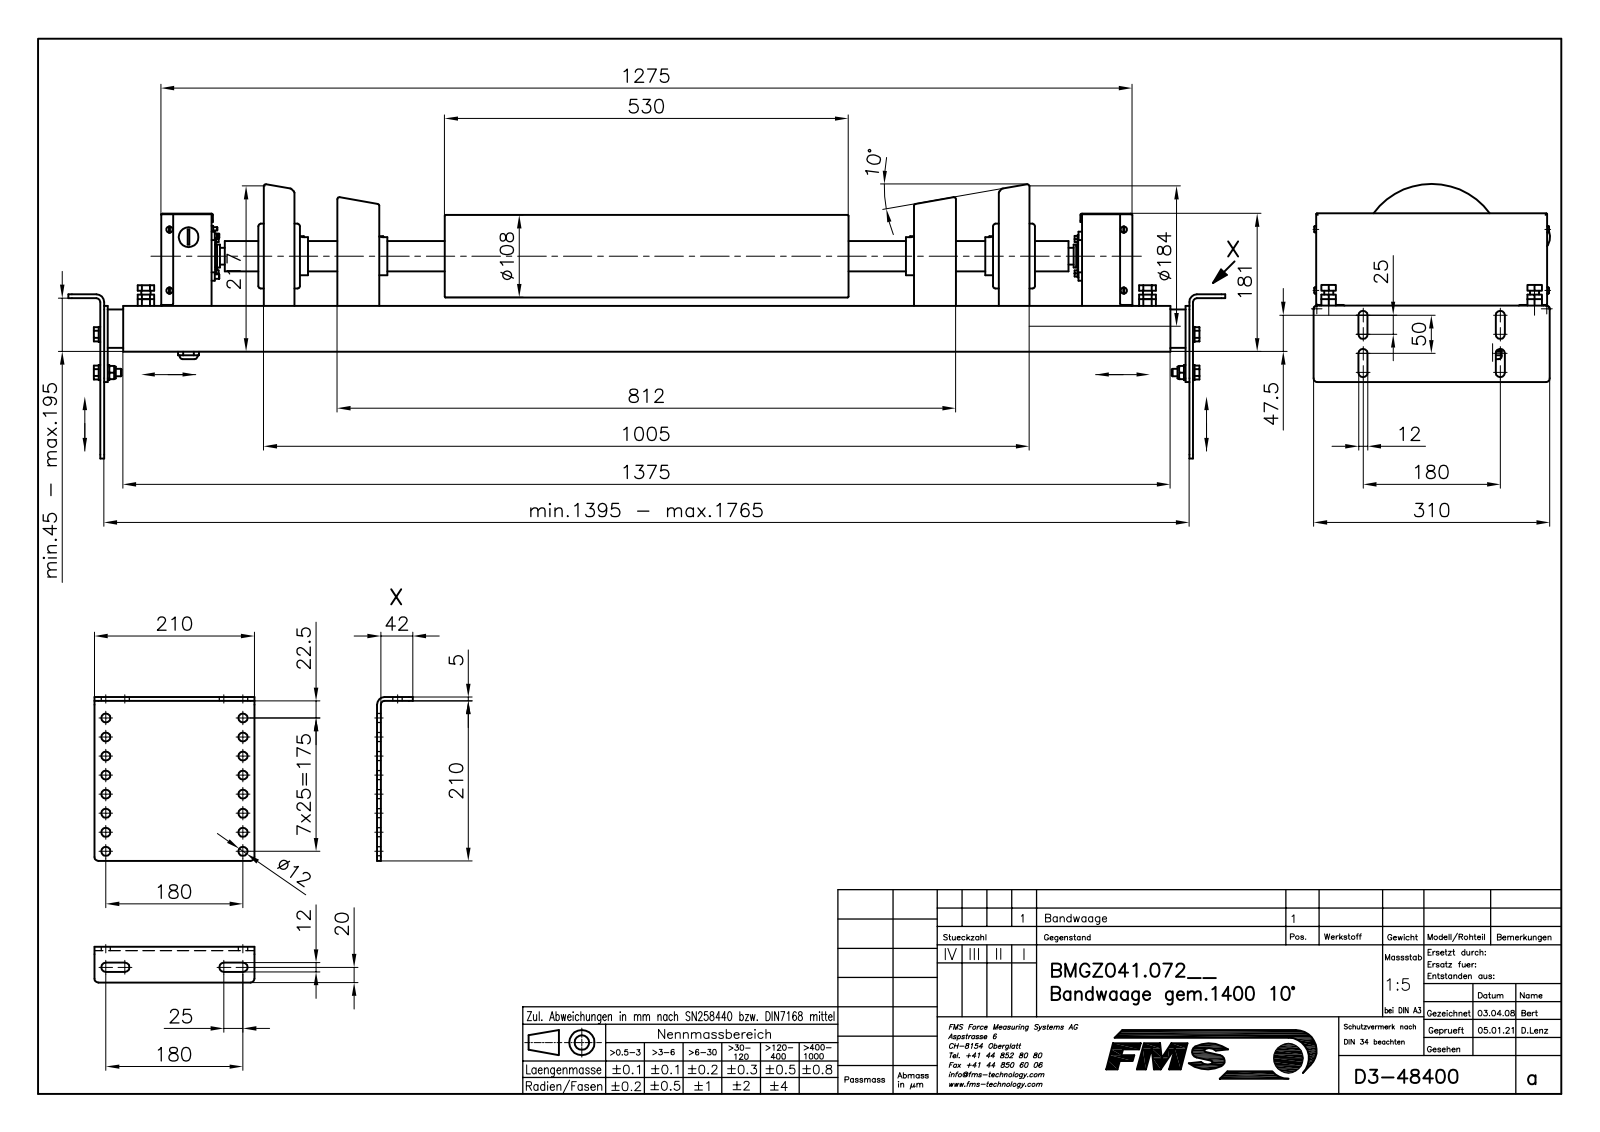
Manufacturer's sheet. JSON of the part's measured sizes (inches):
{"part_name": "B48400_STP; B50121; B48277; TEIL1 (+8 more)", "step_written_by": "Mechanical Desktop 2009 (CONFIG_CONTROL_DESIGN)", "units": "inches", "bodies": {"solids": 179, "faces": 2936, "planar": 1427, "cylindrical": 1062, "other": 447}, "overall_size": [59.803, 14.154, 12.213], "volume_in3": 539.1, "surface_area_in2": 5848, "round_holes": [[0.472, 17], [0.197, 6], [0.138, 4], [0.193, 4], [0.252, 4], [0.272, 4], [0.342, 4], [0.344, 4], [0.394, 4], [0.413, 4], [0.42, 4], [0.583, 4]], "round_bosses_or_shafts": [[0.472, 11], [0.323, 8], [0.165, 8], [0.787, 6], [0.394, 6], [0.315, 6], [0.197, 5], [0.63, 4]], "partial_cylinders_radius": [[0.079, 34], [0.039, 24], [0.157, 16], [0.197, 16], [0.236, 14], [0.138, 8], [0.089, 6], [0.02, 4]], "face_to_face_distances": [0.157, 0.197, 10.63, 1.417, 0.039, 1.26, 10.472, 2.205, 1.575, 0.118], "hole_center_spacings": [0.984, 7.155, 1.969, 2.953, 7.355, 7.677, 3.937, 7.087]}
